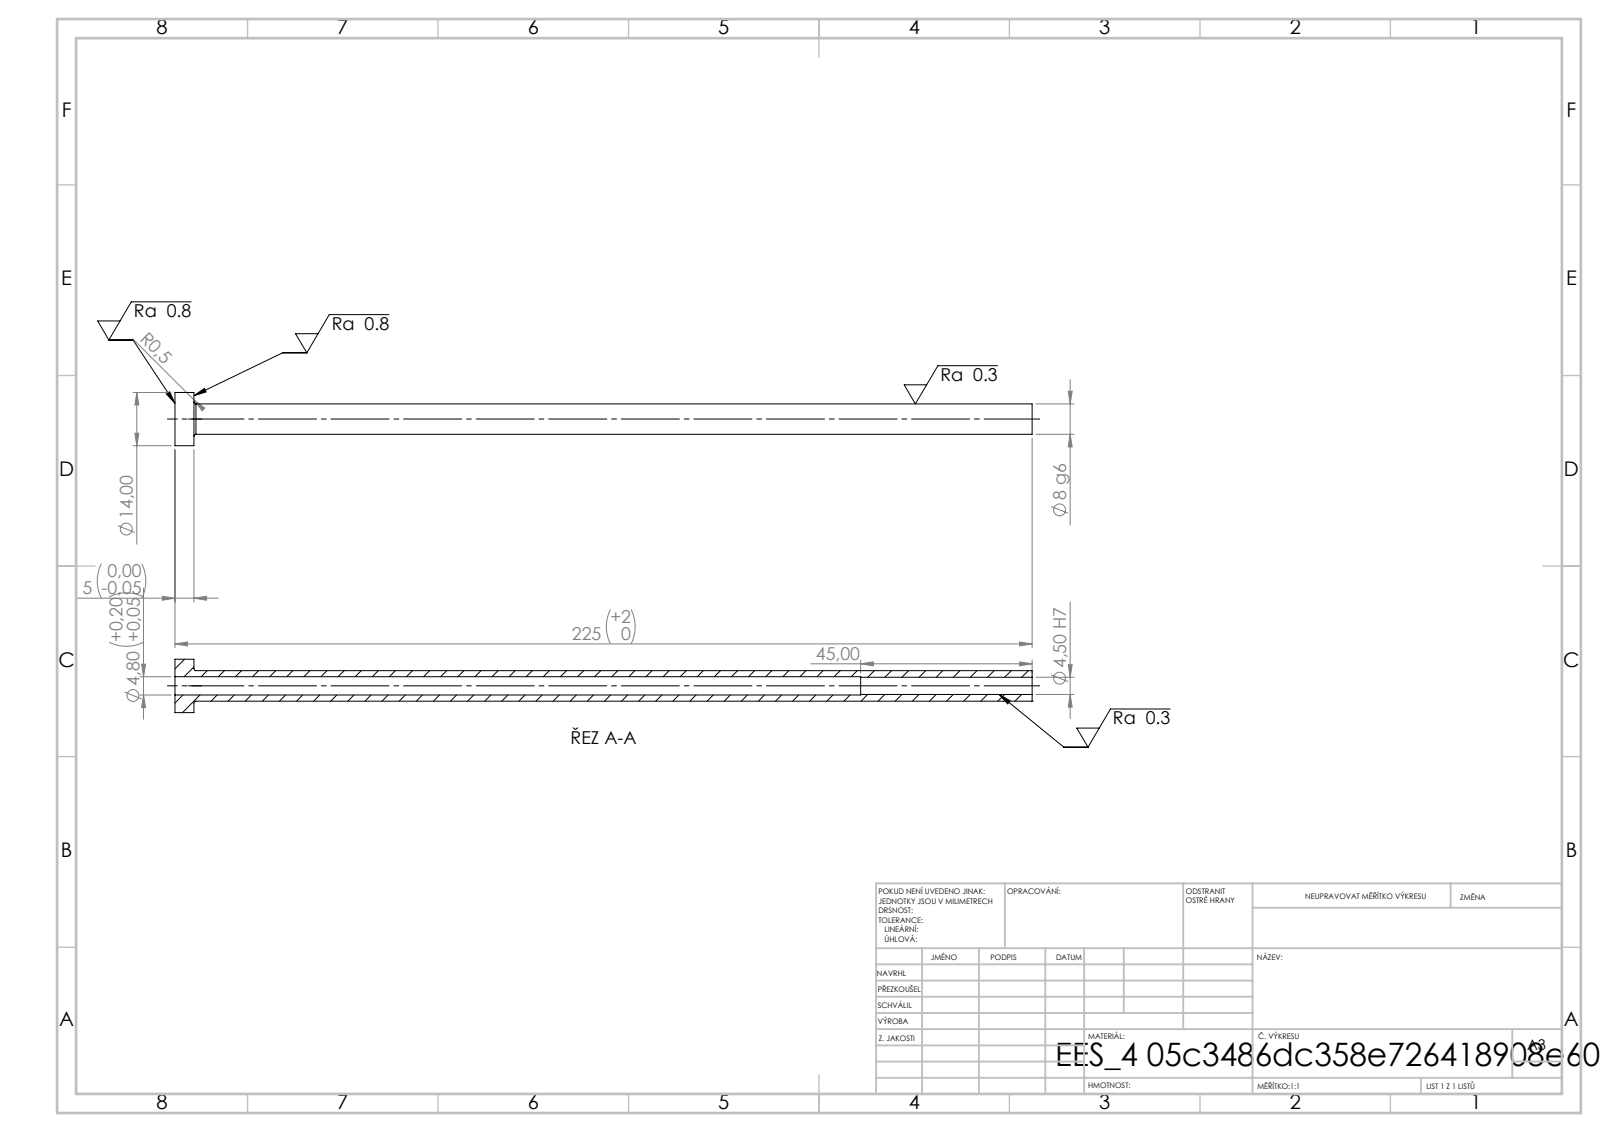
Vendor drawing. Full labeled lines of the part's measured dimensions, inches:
STEP written by: SolidWorks 2019 (CONFIG_CONTROL_DESIGN)
Units: inches
Bodies: 1 solid, 14 faces (4 planar, 8 cylindrical, 2 other)
Overall size (bounding box): 8.858 × 0.551 × 0.551
Volume: 0.479 in³ · Surface area: 14.52 in²
Round holes (diameter × count): ⌀0.177 ×1, ⌀0.189 ×1
Round bosses / shafts (diameter × count): ⌀0.551 ×1, ⌀0.315 ×1
Main face-to-face distances: 0.197, 8.858, 8.661, 7.087, 6.89, 1.772
